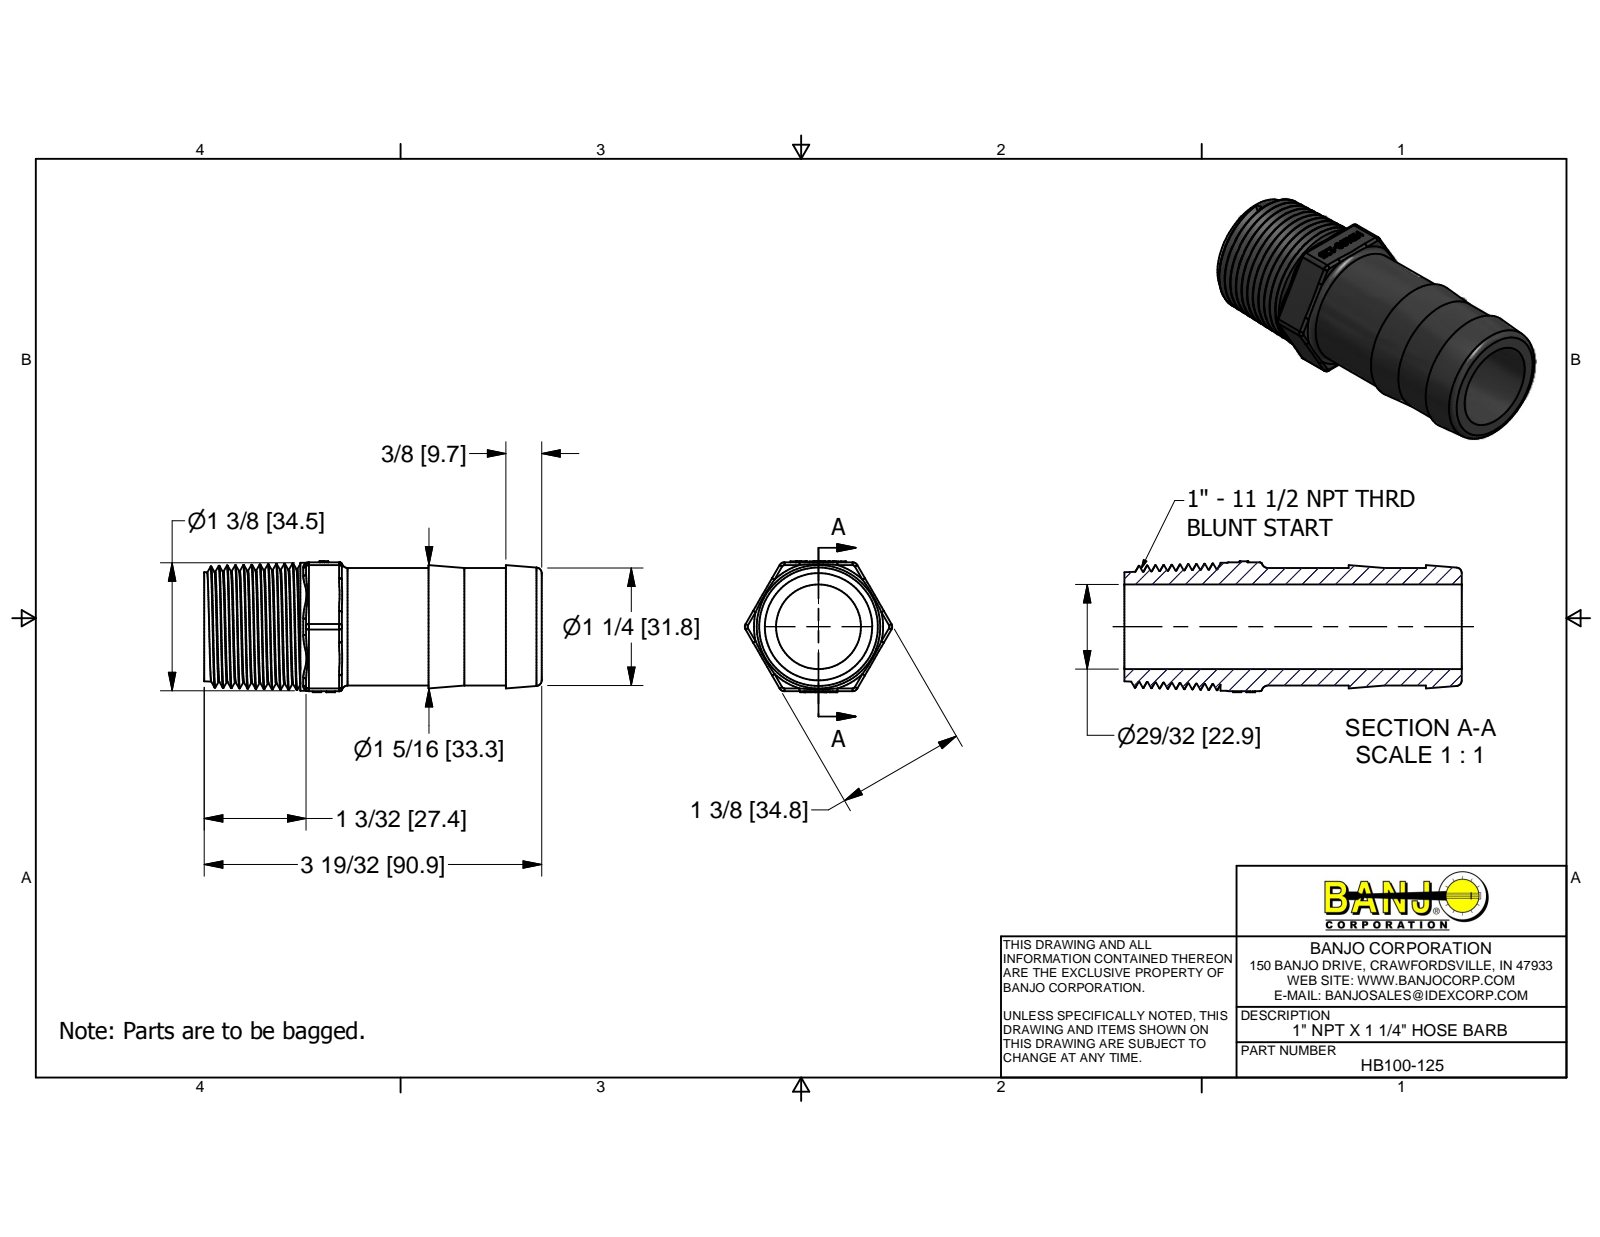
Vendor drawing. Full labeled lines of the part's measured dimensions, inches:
Part name (STEP PRODUCT): HB100-125
STEP written by: Autodesk Inventor 2013 (AUTOMOTIVE_DESIGN)
Units: inches
Bodies: 1 solid, 348 faces (161 planar, 28 cylindrical, 159 other)
Overall size (bounding box): 3.58 × 1.563 × 1.39
Volume: 2.325 in³ · Surface area: 29.43 in²
Round holes (diameter × count): ⌀0.9 ×1
Round bosses / shafts (diameter × count): ⌀1.36 ×1, ⌀1.25 ×1
Partial cylindrical surfaces — rounded edges, fillets, slot ends (radius × count): R0.03 ×12, R0.06 ×6
Main face-to-face distances: 1.37, 3.58, 2.56, 1.02, 0.38, 1.2, 2.38, 0.82, 2.18, 3.2
